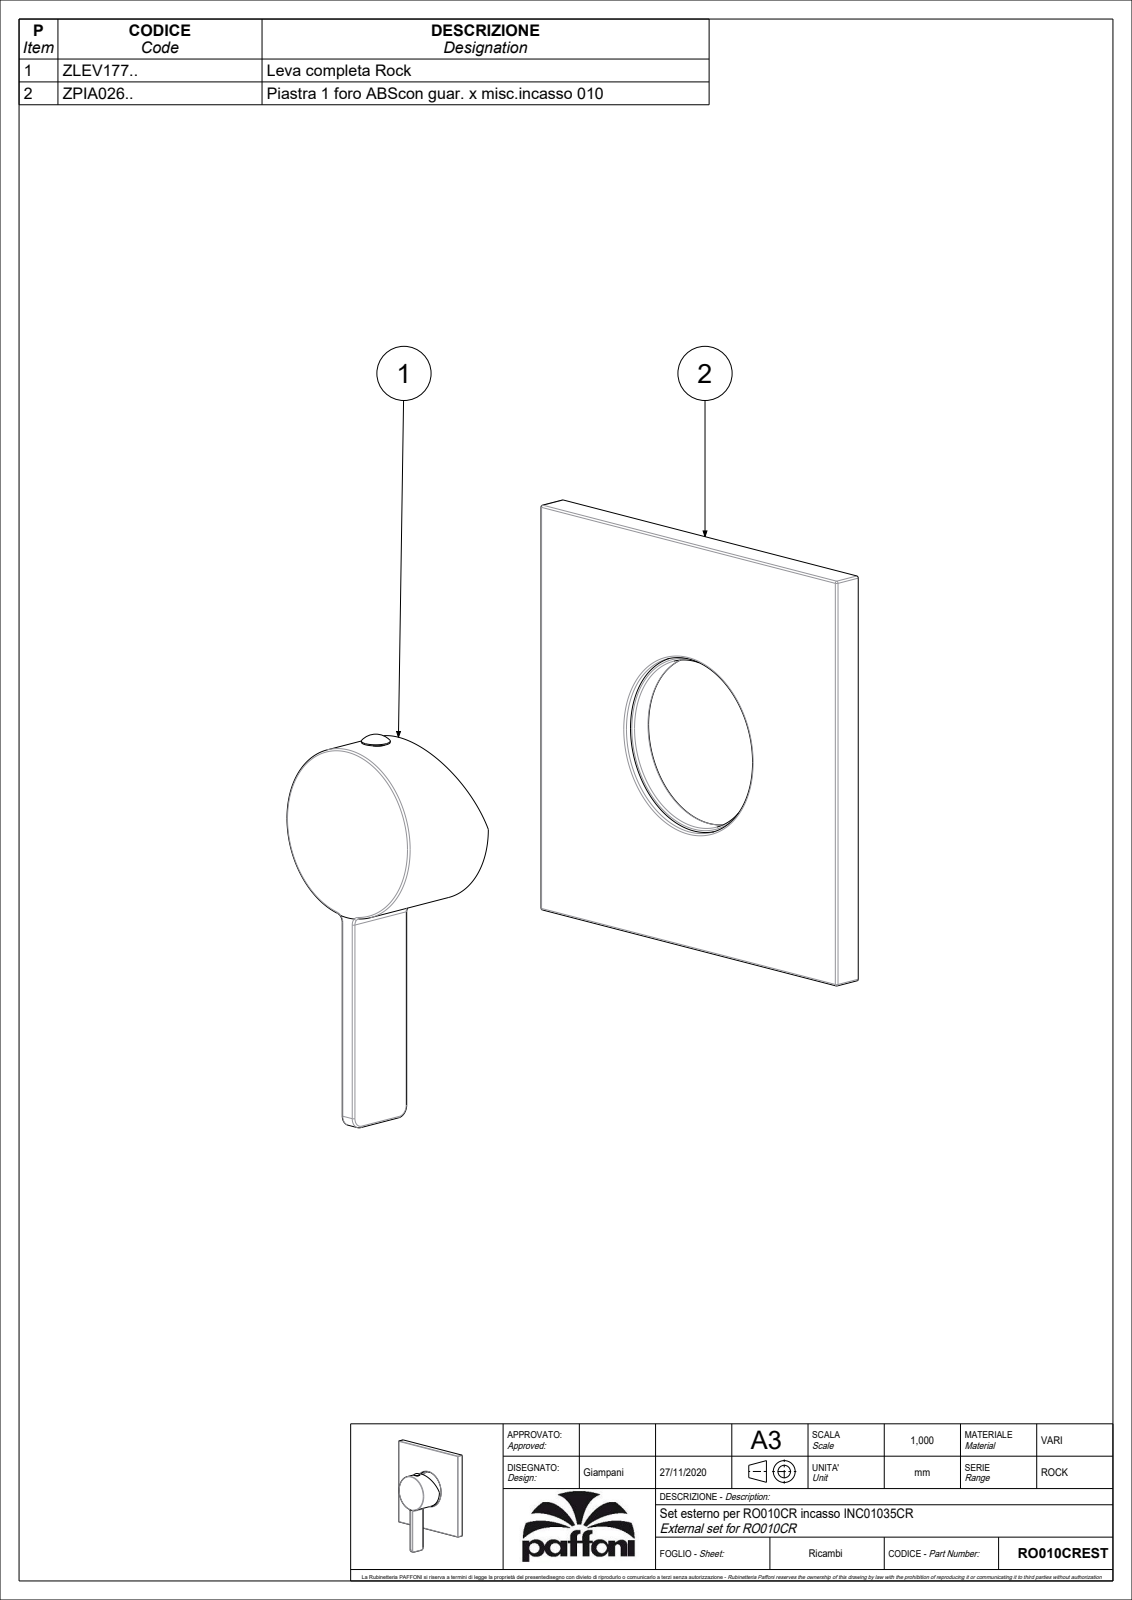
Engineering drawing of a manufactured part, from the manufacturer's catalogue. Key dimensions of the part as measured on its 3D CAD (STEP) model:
Part name (STEP PRODUCT): RO010CREST
STEP written by: CREO PARAMETRIC BY PTC INC, 2020044 (CONFIG_CONTROL_DESIGN)
Units: millimetres
Bodies: 2 solids, 208 faces (73 planar, 71 cylindrical, 64 other)
Overall size (bounding box): 135 × 110 × 40
Volume: 80 070 mm³ · Surface area: 47 343 mm²
Round holes (diameter × count): ⌀3 ×1, ⌀45 ×1, ⌀47 ×1, ⌀49 ×1
Round bosses / shafts (diameter × count): ⌀51 ×1, ⌀45.5 ×1, ⌀7.6 ×1, ⌀5.5 ×1, ⌀5 ×1
Partial cylindrical surfaces — rounded edges, fillets, slot ends (radius × count): R0.5 ×25, R2 ×6, R1 ×4, R0.3 ×2, R1.5 ×2, R3 ×2, R3.5 ×1
Main face-to-face distances: 7, 2, 5, 108, 2.5, 0.5, 107.5, 105.5, 52.75, 57.25
